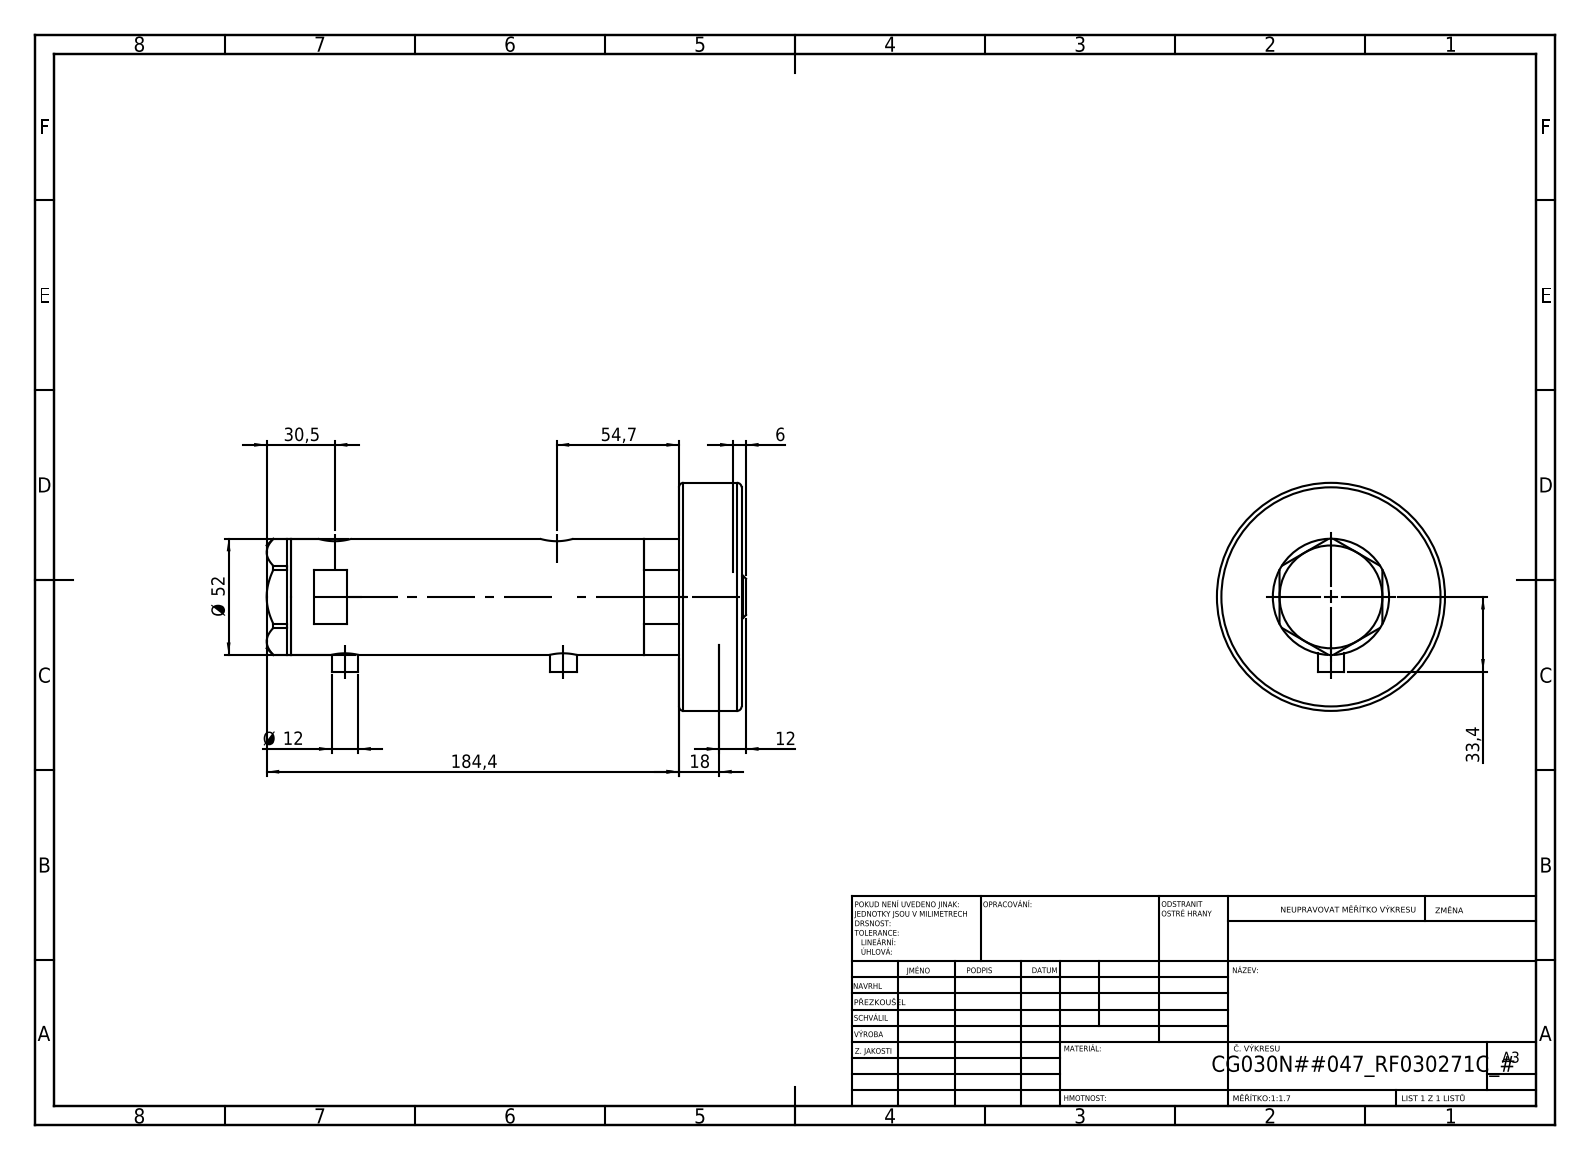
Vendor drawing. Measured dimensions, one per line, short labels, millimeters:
name: V270CG_MIDDLE; V270CG_FRONT; V270CG_271C; V270CG_VC (+1 more)
written by: SolidWorks 2019 (CONFIG_CONTROL_DESIGN)
unit: mm
bodies: 5 solids, 144 faces (67 planar, 53 cylindrical, 24 other)
size: 214.4 × 102 × 102
volume: 585 020 mm³; area: 112 923 mm²
holes: 2× ⌀9.73, 2× ⌀12.5, 2× ⌀15, 1× ⌀6.5, 1× ⌀20, 1× ⌀21.5, 1× ⌀30, 1× ⌀33, 1× ⌀40, 1× ⌀44
bosses: 2× ⌀12, 1× ⌀102, 1× ⌀52, 1× ⌀38, 1× ⌀19
face distances: 28, 173.4, 201.4, 121.5, 51.9, 79.9, 23.8, 97.7, 149.6, 177.6
hole spacings: 2.9, 4.5, 94.7, 97.6, 99.2, 102.1
